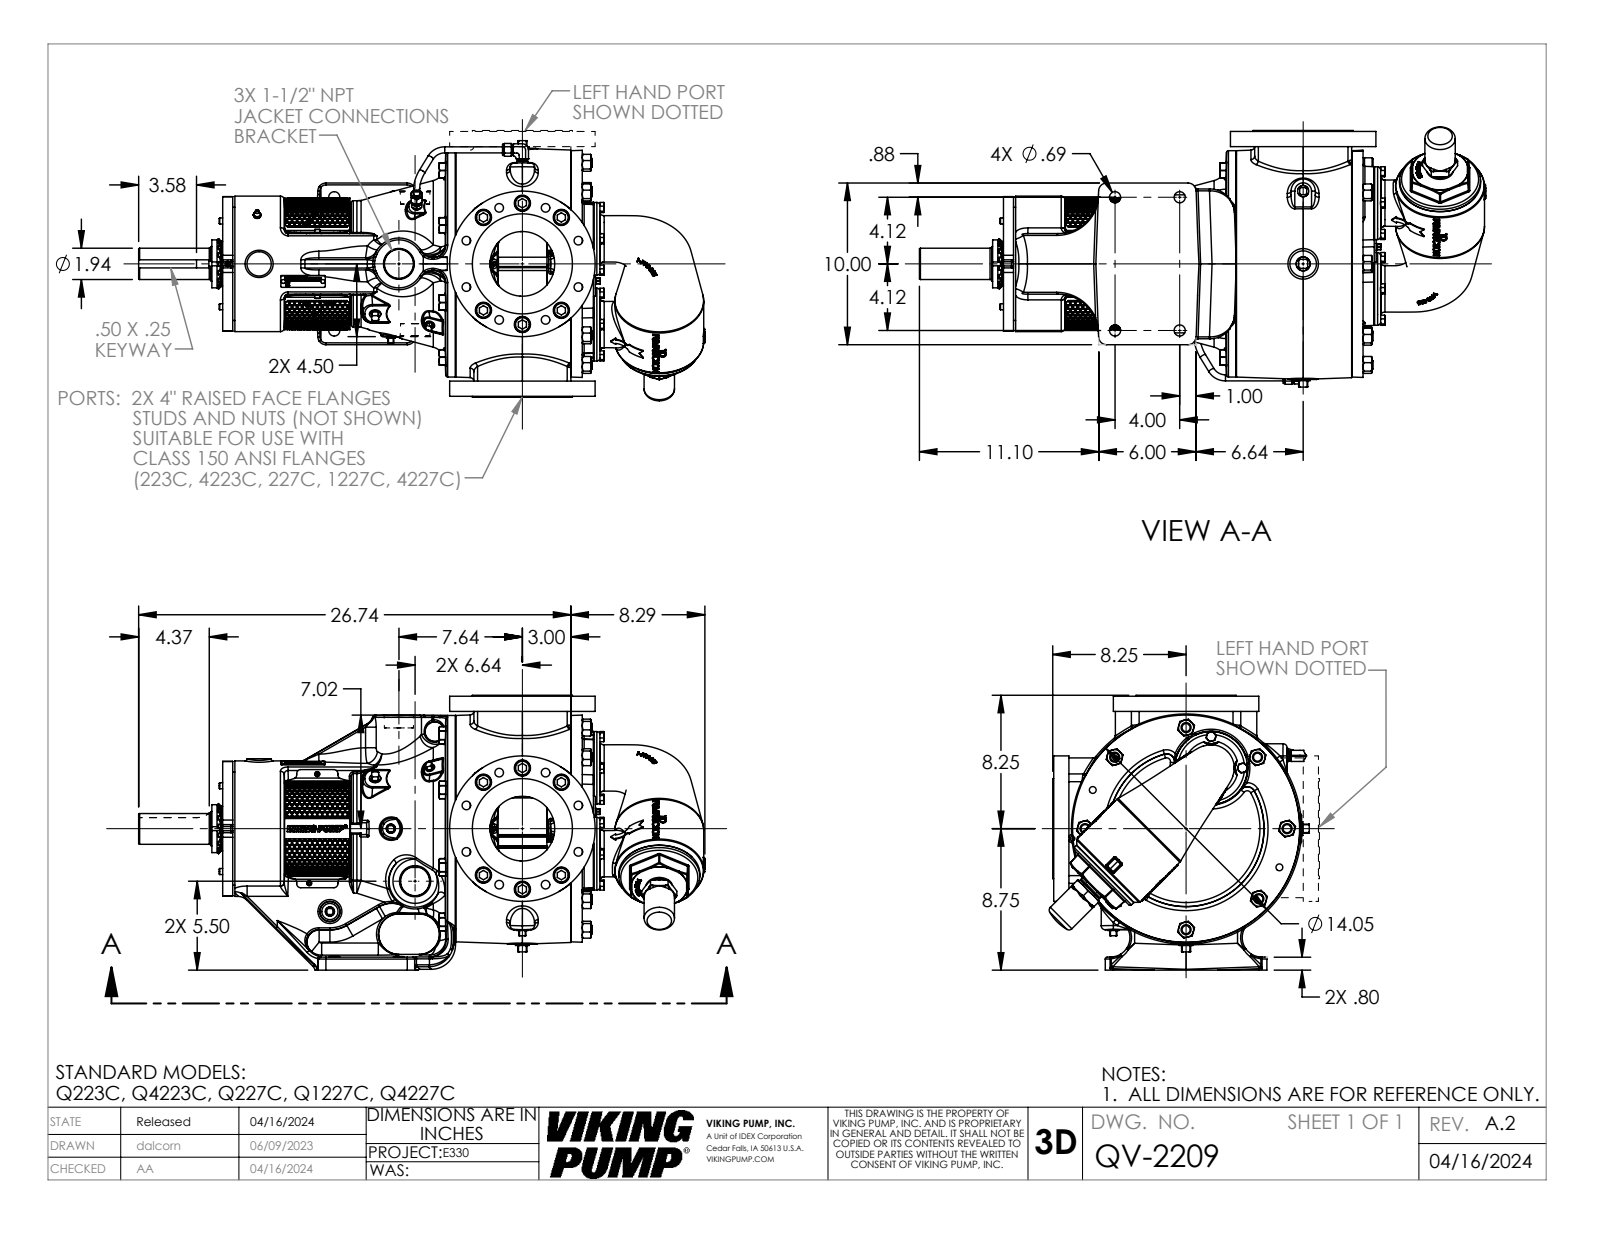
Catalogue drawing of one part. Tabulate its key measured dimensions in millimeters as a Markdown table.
| quantity | value |
| --- | --- |
| part name | QV-2209 |
| STEP written by | SolidWorks 2022 (AUTOMOTIVE_DESIGN) |
| units | millimeters |
| bodies | 1 solid, 8512 faces (3180 planar, 712 cylindrical, 4620 other) |
| overall size | 890.08 × 431.8 × 411.88 |
| volume | 41 940 000 mm³ |
| surface area | 1 432 000 mm² |
| round holes (diameter × count) | 13.49 × 16, 25.4 × 12, 6.76 × 8, 29.38 × 8, 6.35 × 6, 17.48 × 4, 4.04 × 2, 7.94 × 2, 8.38 × 2, 101.6 × 2, 5.41 × 1, 11.51 × 1 |
| round bosses / shafts (diameter × count) | 23.81 × 12, 15.68 × 8, 11.11 × 3, 7.92 × 3, 228.6 × 2, 157.23 × 2, 114.3 × 2, 9.53 × 2 |
| partial cylindrical surfaces (radius × count) | 3.05 × 52, 1.52 × 30, 12.7 × 22, 0.38 × 18, 2.34 × 18, 6.35 × 17, 19.05 × 16, 0.76 × 12 |
| main face-to-face distances | 23.88, 95.25, 12.7, 25.4, 1.52, 552.6, 565.3, 430.28, 457.35, 470.05 |
| hole center spacings | 95.25, 134.7, 72.9, 176, 52.8, 146.89, 190.5, 37.16 |
